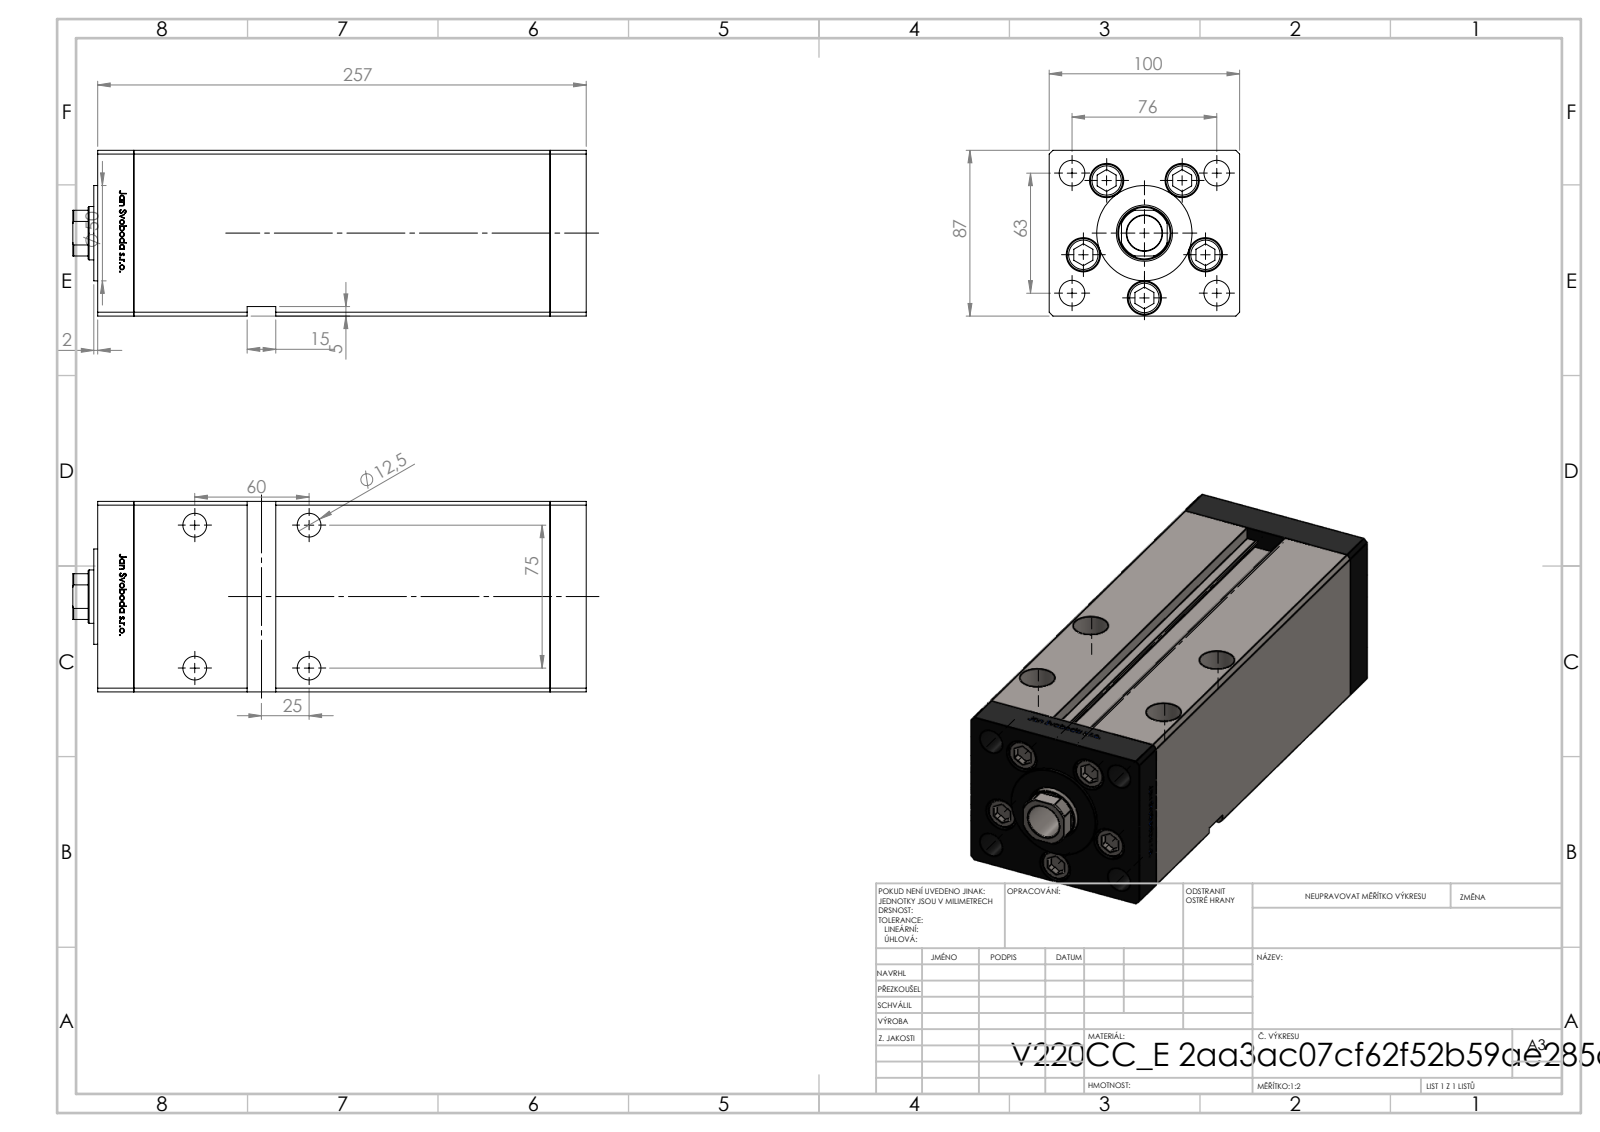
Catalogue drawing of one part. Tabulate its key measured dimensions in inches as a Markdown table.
| quantity | value |
| --- | --- |
| part name | V220C_FRONT_E; V220C BACK_E; V220C_VC_E; V220C_E MIDDLE (+1 more) |
| STEP written by | SolidWorks 2019 (CONFIG_CONTROL_DESIGN) |
| units | inches |
| bodies | 14 solids, 1212 faces (473 planar, 165 cylindrical, 574 other) |
| overall size | 10.61 × 3.937 × 3.425 |
| volume | 113.8 in³ |
| surface area | 411.9 in² |
| round holes (diameter × count) | 0.531 × 11, 0.709 × 5, 0.728 × 5, 0.492 × 4, 0.079 × 2, 0.518 × 2, 1.102 × 1, 1.161 × 1 |
| round bosses / shafts (diameter × count) | 0.669 × 5, 0.315 × 5, 1.969 × 1 |
| partial cylindrical surfaces (radius × count) | 0.037 × 2, 0.531 × 1 |
| main face-to-face distances | 3.937, 3.425, 0.748, 8.602, 9.35, 1.348, 10.098, 0.6, 8.002, 8.75 |
| hole center spacings | 1.339, 0.732, 1.561, 1.943, 2.281, 0.828, 1.499, 1.546 |
